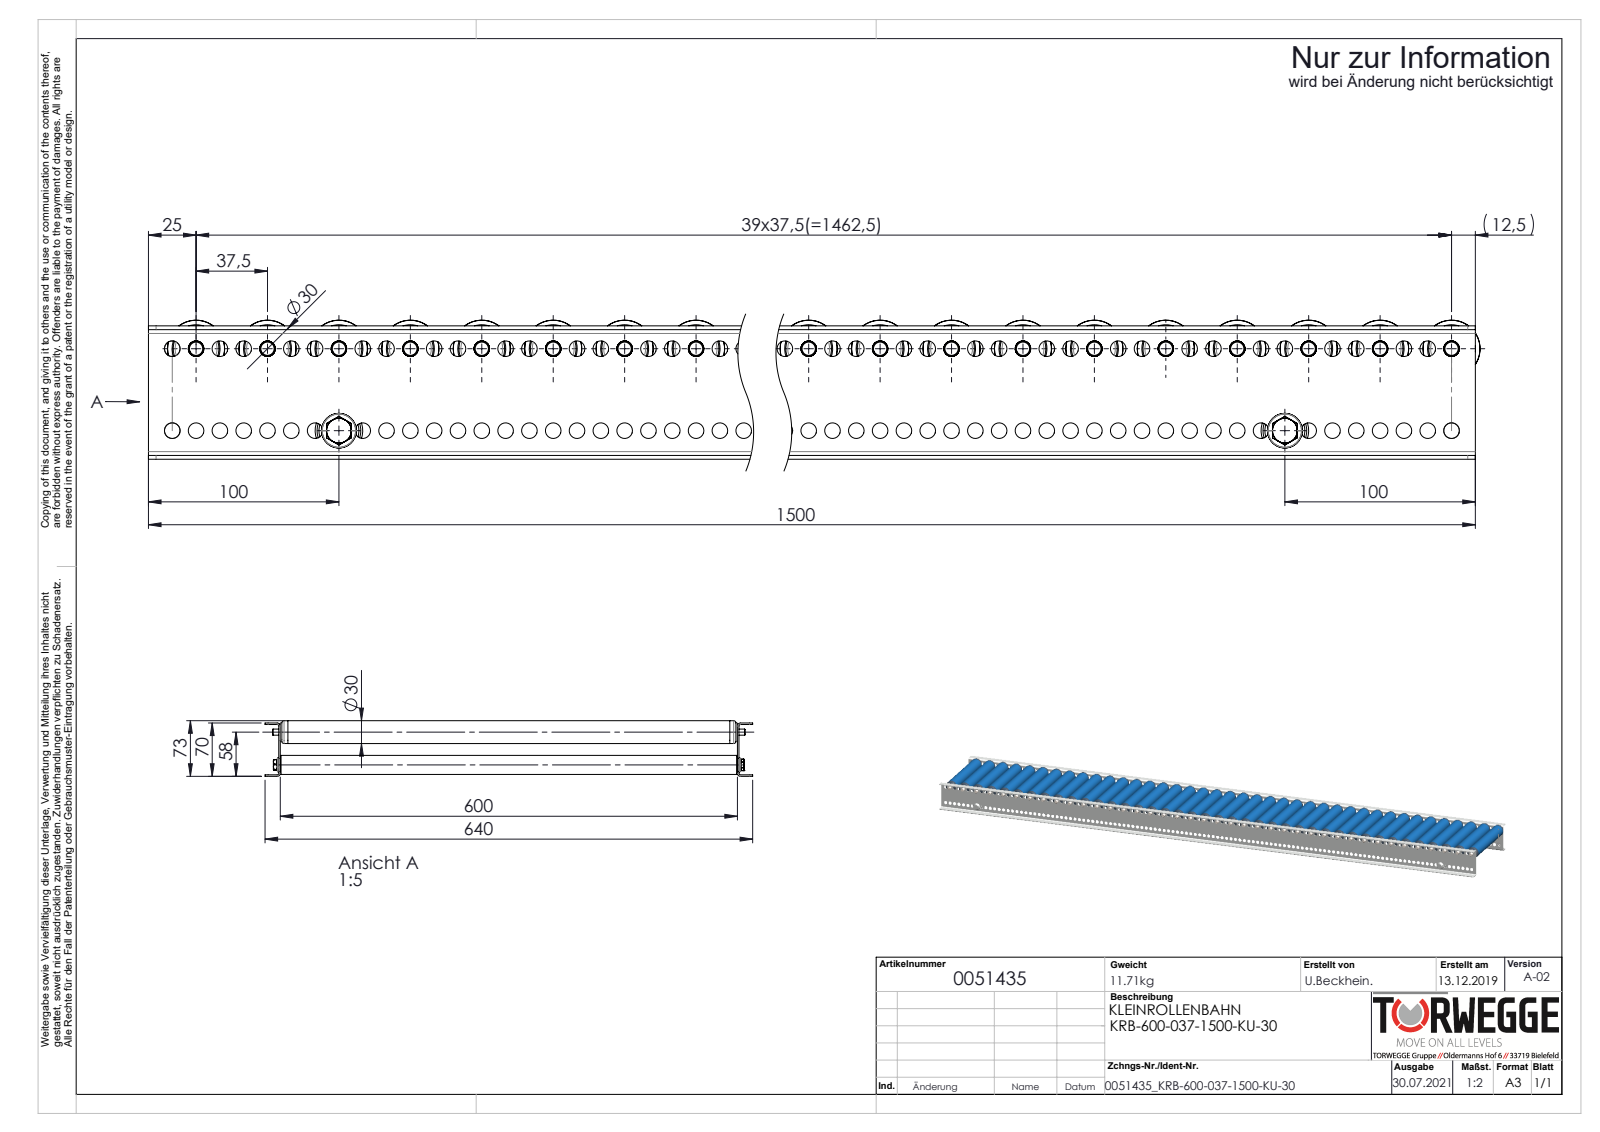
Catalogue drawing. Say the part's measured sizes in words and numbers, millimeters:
The part is named "0039778-Achse-ST-Ø08-KFG_AL620-G-FA; KUT50-30x1,8-KB-A8-FA_KFG_S100902_KUT50-30x1,8-KB-A8-FA-EL=600; 0017013_Tragrollenrohr-Ø30x1,8KU_KFG_L=580; S100995_TYP-KUT50-30x1,8-A8 (+4 more)". Its 3-D file was written by "SolidWorks 2020 (AUTOMOTIVE_DESIGN)". It is 92 solids with 9472 faces: 2920 planar, 3568 cylindrical and 2984 other. Overall it measures 1502.5 by 640 by 73 millimeters. Its volume is 5 718 000 cubic millimeters and its surface area 6 010 000 square millimeters. Round holes: 238 of diameter 8.2, 40 of diameter 8.1, 40 of diameter 22.6, 40 of diameter 25.2, 2 of diameter 6.8, 2 of diameter 21. Round bosses or shafts: 42 of diameter 8, 40 of diameter 30, 40 of diameter 29.9, 40 of diameter 26.5, 40 of diameter 26.4, 40 of diameter 24, 2 of diameter 25. Partial cylindrical surfaces (rounded edges, fillets, slot ends): 40 of radius 5.05, 8 of radius 4, 4 of radius 2. The main face-to-face distances are 2, 602, 600, 68, 604, 70, 66, 10, 590, 12. The hole center spacings are 12.5, 25, 37.5, 50, 62.5, 75, 87.5, 100.
